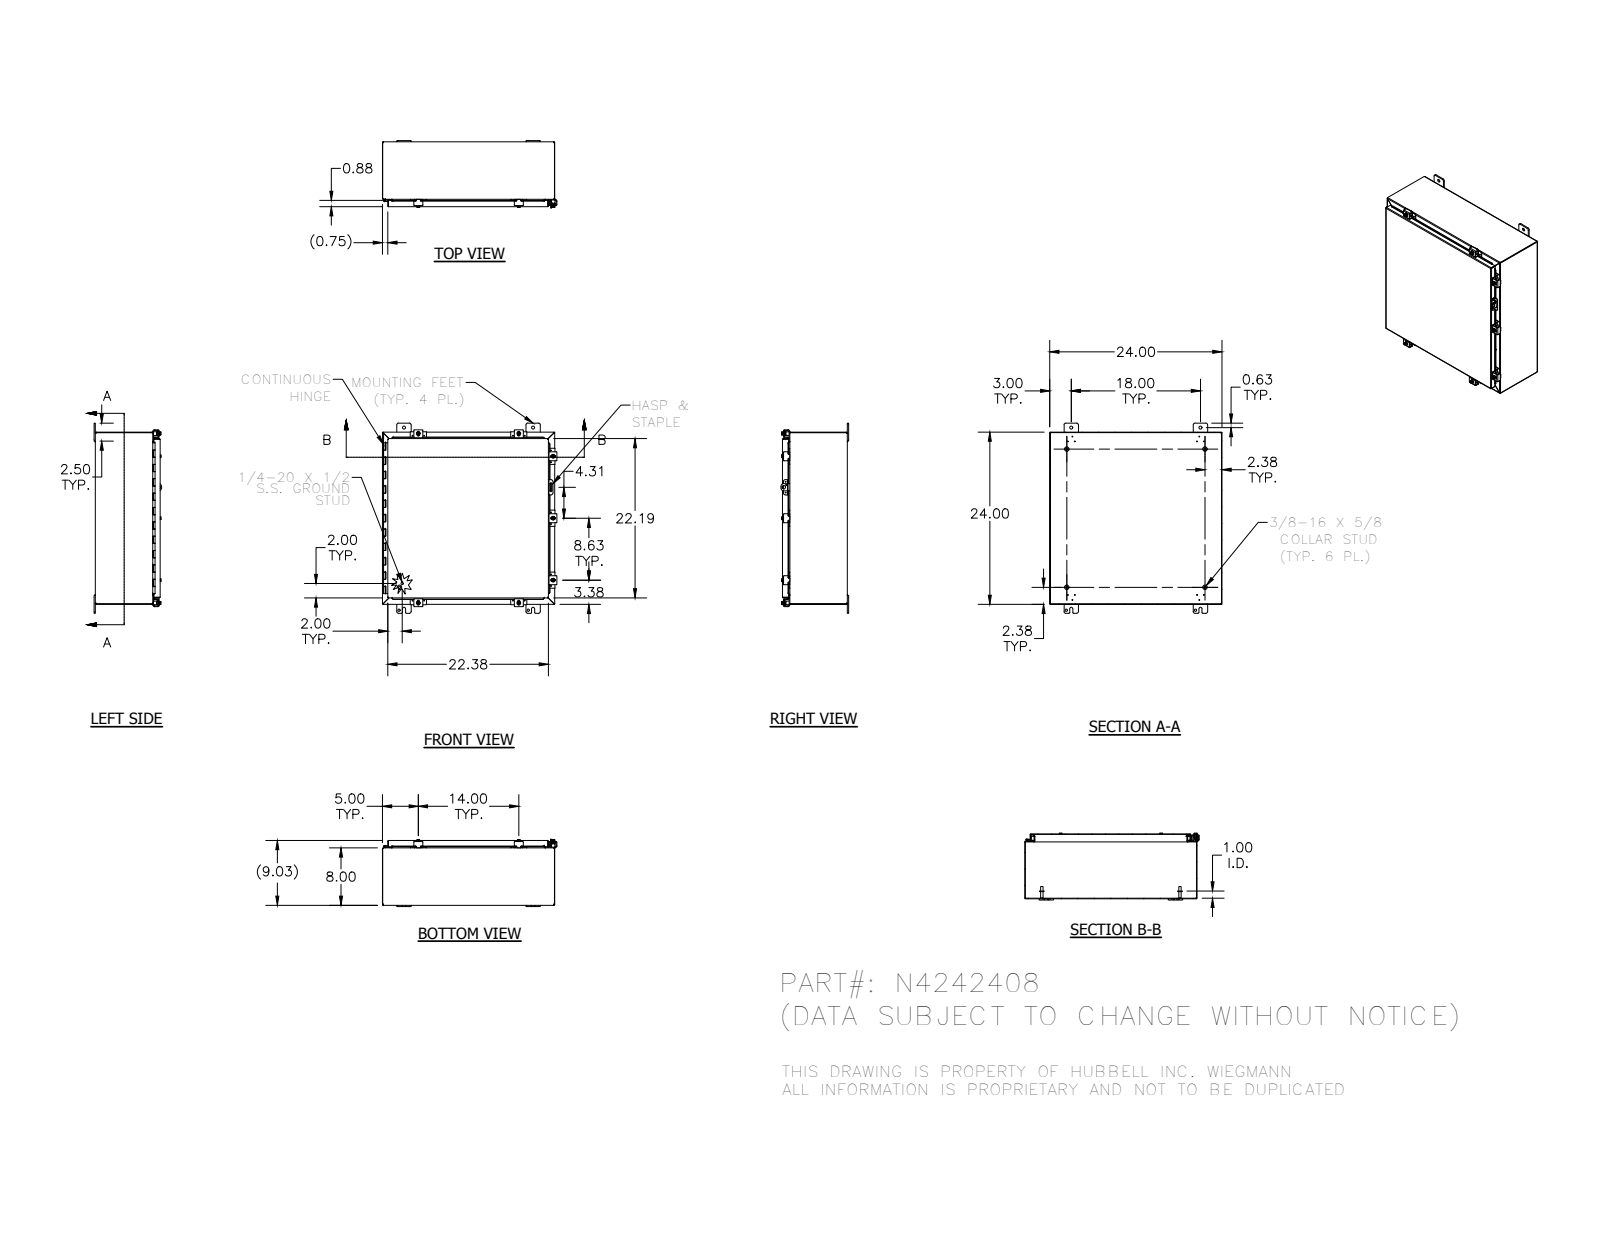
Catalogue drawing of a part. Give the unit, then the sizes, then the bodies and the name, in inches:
Units: inches
Overall size (bounding box): 26.5 × 24.311 × 9.41
Round holes (diameter × count): ⌀0.11 ×17, ⌀0.12 ×12, ⌀0.211 ×7, ⌀0.281 ×7, ⌀0.3 ×7, ⌀0.313 ×4, ⌀0.438 ×4, ⌀0.125 ×1, ⌀0.156 ×1, ⌀0.5 ×1
Round bosses / shafts (diameter × count): ⌀0.25 ×9, ⌀0.52 ×7, ⌀0.5 ×7, ⌀0.35 ×7, ⌀0.625 ×4, ⌀0.33 ×4, ⌀0.115 ×2, ⌀0.337 ×1
Partial cylindrical surfaces — rounded edges, fillets, slot ends (radius × count): R0.03 ×83, R0.062 ×47, R0.125 ×37, R0.25 ×33, R0.031 ×23, R0.105 ×23, R0.141 ×14, R0.1 ×10
Main face-to-face distances: 0.074, 8.959, 23.926, 8.885, 9.033, 23.852, 24, 7.926, 1.033, 8
Hole centre spacings: 18, 0.876, 0.759, 0.839, 0.94, 0.969, 1.593, 1.995
Volume: 176.4 in³ · Surface area: 4 606 in²
Bodies: 52 solids, 2242 faces (856 planar, 1003 cylindrical, 383 other)
Part name (STEP PRODUCT): HFW30825-3_1; 38420_1; 388116_1; HFW30825-4_1 (+8 more)
STEP written by: SolidWorks 2014 (AUTOMOTIVE_DESIGN)
